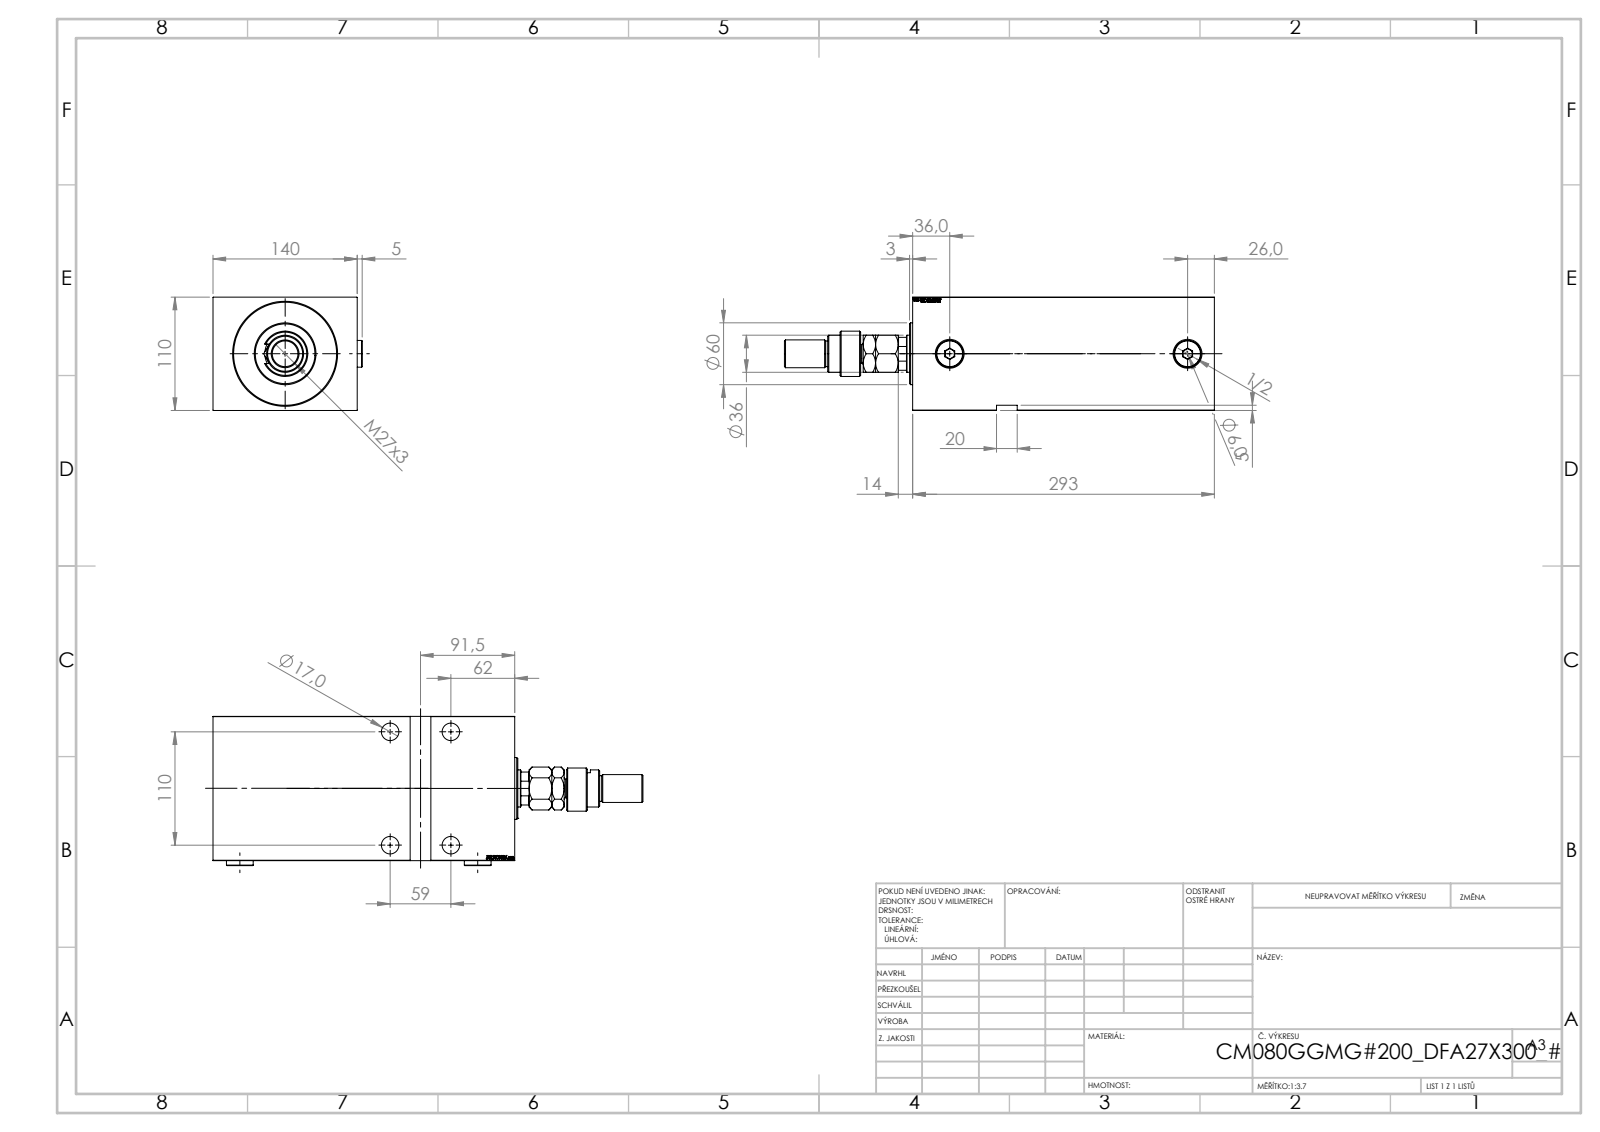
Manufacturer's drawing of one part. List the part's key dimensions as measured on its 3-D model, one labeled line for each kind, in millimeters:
Part name (STEP PRODUCT): V450CM_G_VCP; V450CM_VC_G; MFA; FEMALE_PART_FOR_DFA (+2 more)
STEP written by: SolidWorks 2019 (CONFIG_CONTROL_DESIGN)
Units: millimetres
Bodies: 7 solids, 981 faces (470 planar, 69 cylindrical, 442 other)
Overall size (bounding box): 417.5 × 144.9 × 110
Volume: 3 626 000 mm³ · Surface area: 367 056 mm²
Round holes (diameter × count): ⌀17 ×4, ⌀25 ×4, ⌀6 ×2, ⌀20.96 ×2, ⌀28 ×2, ⌀25.5 ×1, ⌀39.5 ×1, ⌀80 ×1, ⌀82 ×1, ⌀100 ×1
Round bosses / shafts (diameter × count): ⌀26 ×2, ⌀60 ×1, ⌀44 ×1, ⌀36 ×1, ⌀28 ×1, ⌀27 ×1, ⌀25 ×1, ⌀18 ×1
Partial cylindrical surfaces — rounded edges, fillets, slot ends (radius × count): R9.5 ×1, R15 ×1, R17.5 ×1
Main face-to-face distances: 110, 140, 5, 293, 21, 272, 288, 267, 79, 58
Hole centre spacings: 59, 110, 124.82, 231
